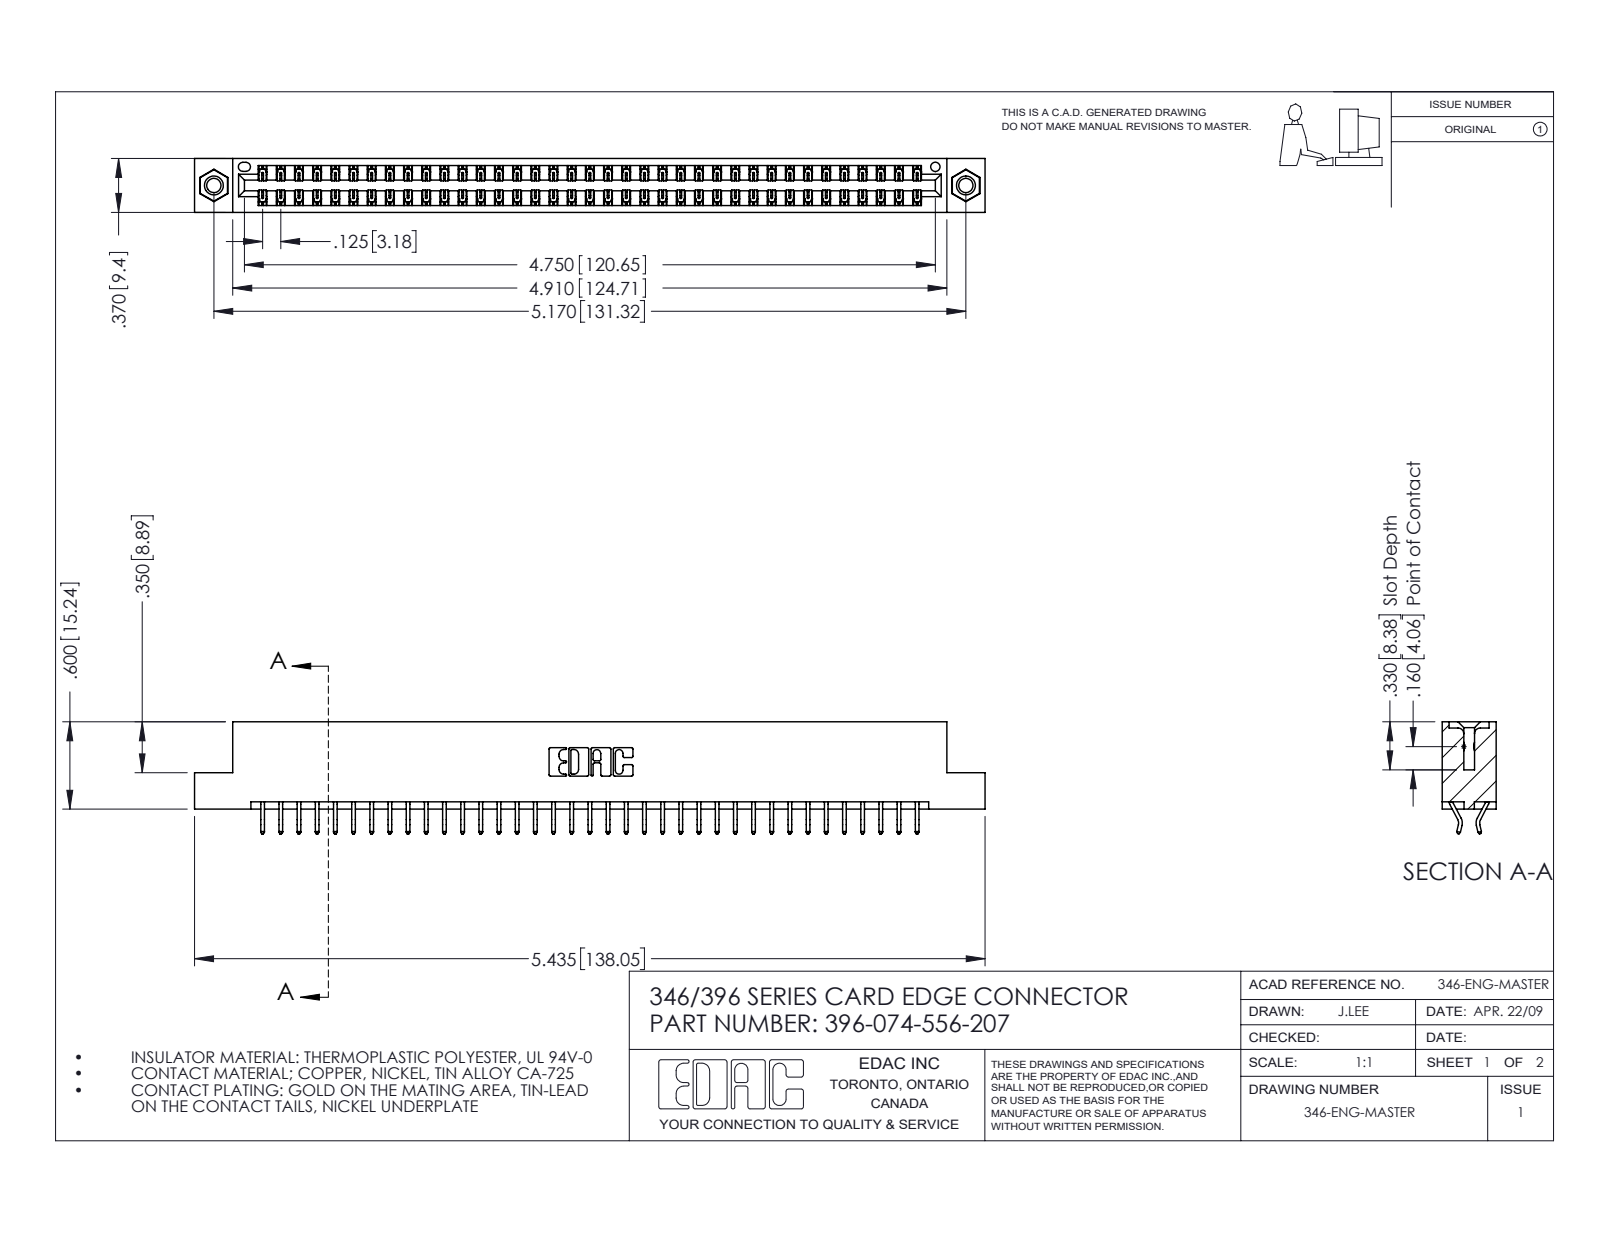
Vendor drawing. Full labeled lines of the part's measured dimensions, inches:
Part name (STEP PRODUCT): 345-292-001_556 Tail; 346 Part_Flush Mounting Lugs - 0.156 Dia-TI; 345-250-001_345-250-005-103; 396-074-556-207
STEP written by: SolidWorks 2016 (CONFIG_CONTROL_DESIGN)
Units: inches
Bodies: 77 solids, 4474 faces (2994 planar, 1464 cylindrical, 16 other)
Overall size (bounding box): 5.435 × 0.77 × 0.37
Volume: 0.818 in³ · Surface area: 28.39 in²
Round holes (diameter × count): ⌀0.098 ×2, ⌀0.125 ×2, ⌀0.156 ×2, ⌀0.064 ×1
Round bosses / shafts (diameter × count): ⌀0.155 ×2
Partial cylindrical surfaces — rounded edges, fillets, slot ends (radius × count): R0.006 ×111, R0.01 ×22, R0.007 ×6, R0.031 ×6, R0.026 ×3, R0.01 ×2, R0.014 ×2, R0.022 ×2
Main face-to-face distances: 0.048, 0.322, 0.37, 0.25, 0.025, 0.072, 0.298, 0.275, 0.148, 0.222
Hole centre spacings: 0.246, 4.961, 5.17
